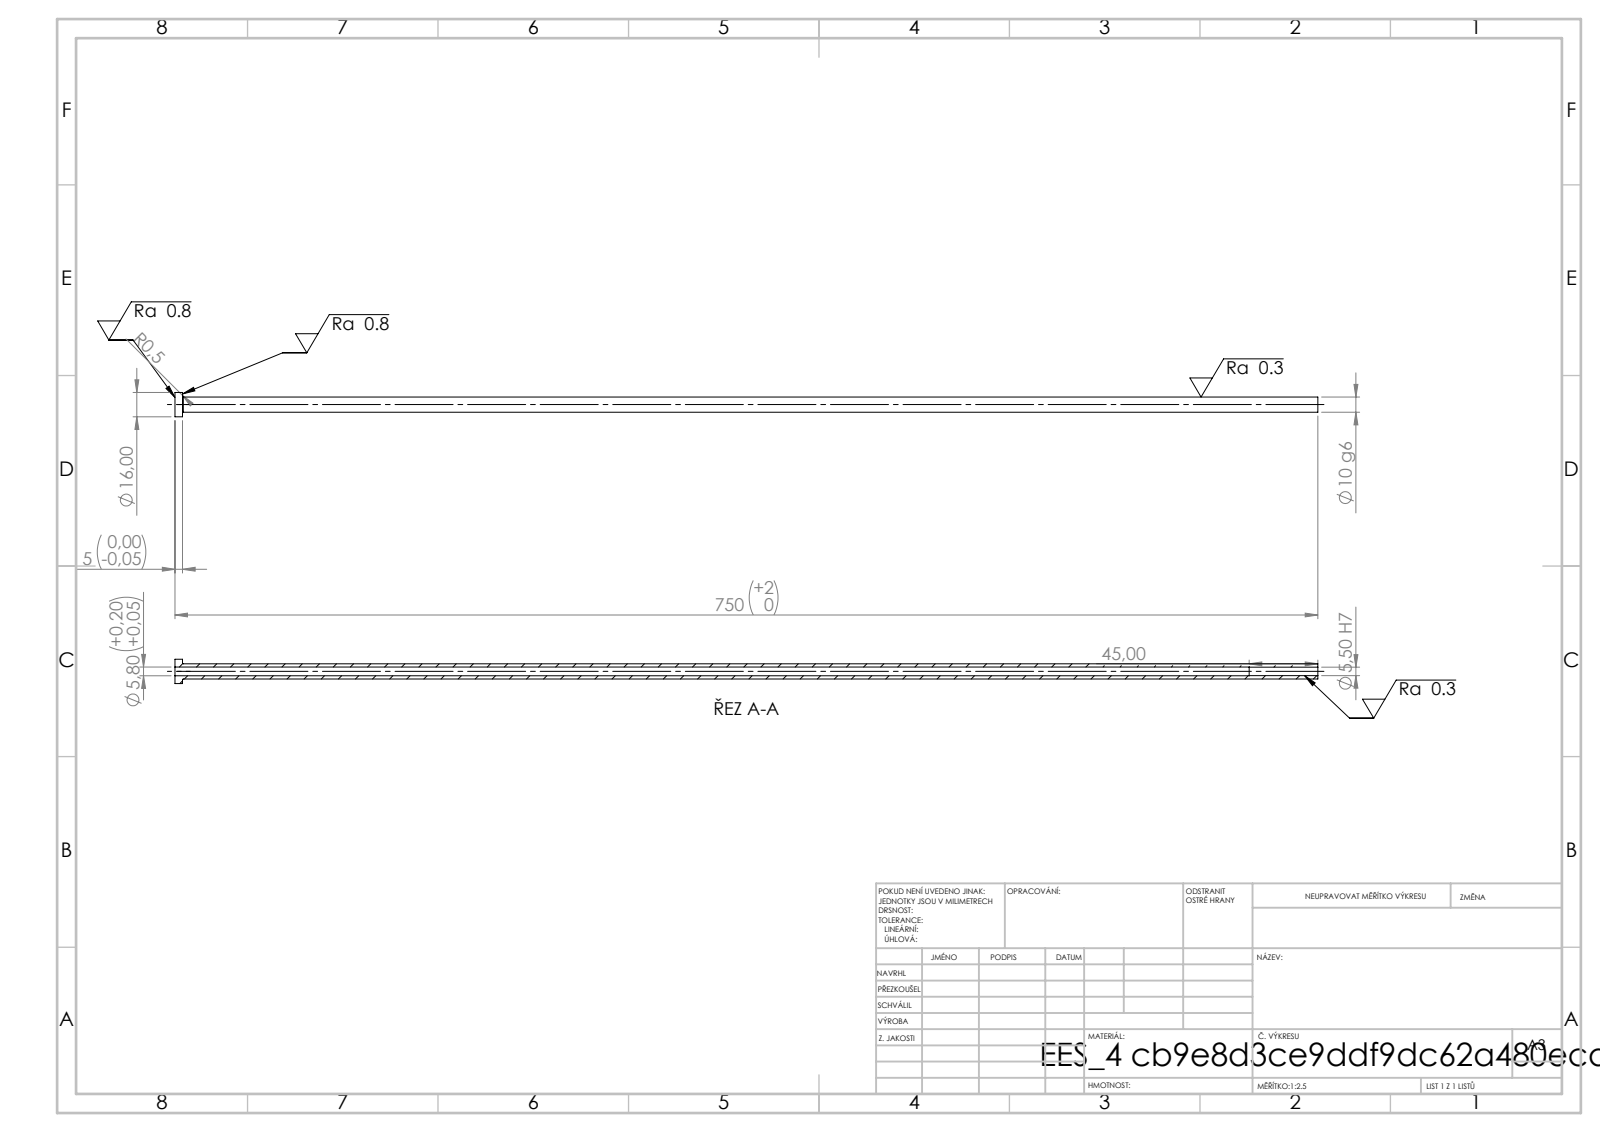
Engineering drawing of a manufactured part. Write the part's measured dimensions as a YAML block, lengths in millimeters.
step_written_by: "SolidWorks 2019 (CONFIG_CONTROL_DESIGN)"
units: millimeters
bodies: {solids: 1, faces: 14, planar: 4, cylindrical: 8, other: 2}
overall_size: [750, 16, 16]
volume: 39823
surface_area: 37628
round_holes:
  - {diameter: 5.5, count: 1}
  - {diameter: 5.8, count: 1}
round_bosses_or_shafts:
  - {diameter: 16, count: 1}
  - {diameter: 10, count: 1}
face_to_face_distances: [5, 750, 745, 705, 700, 45]
